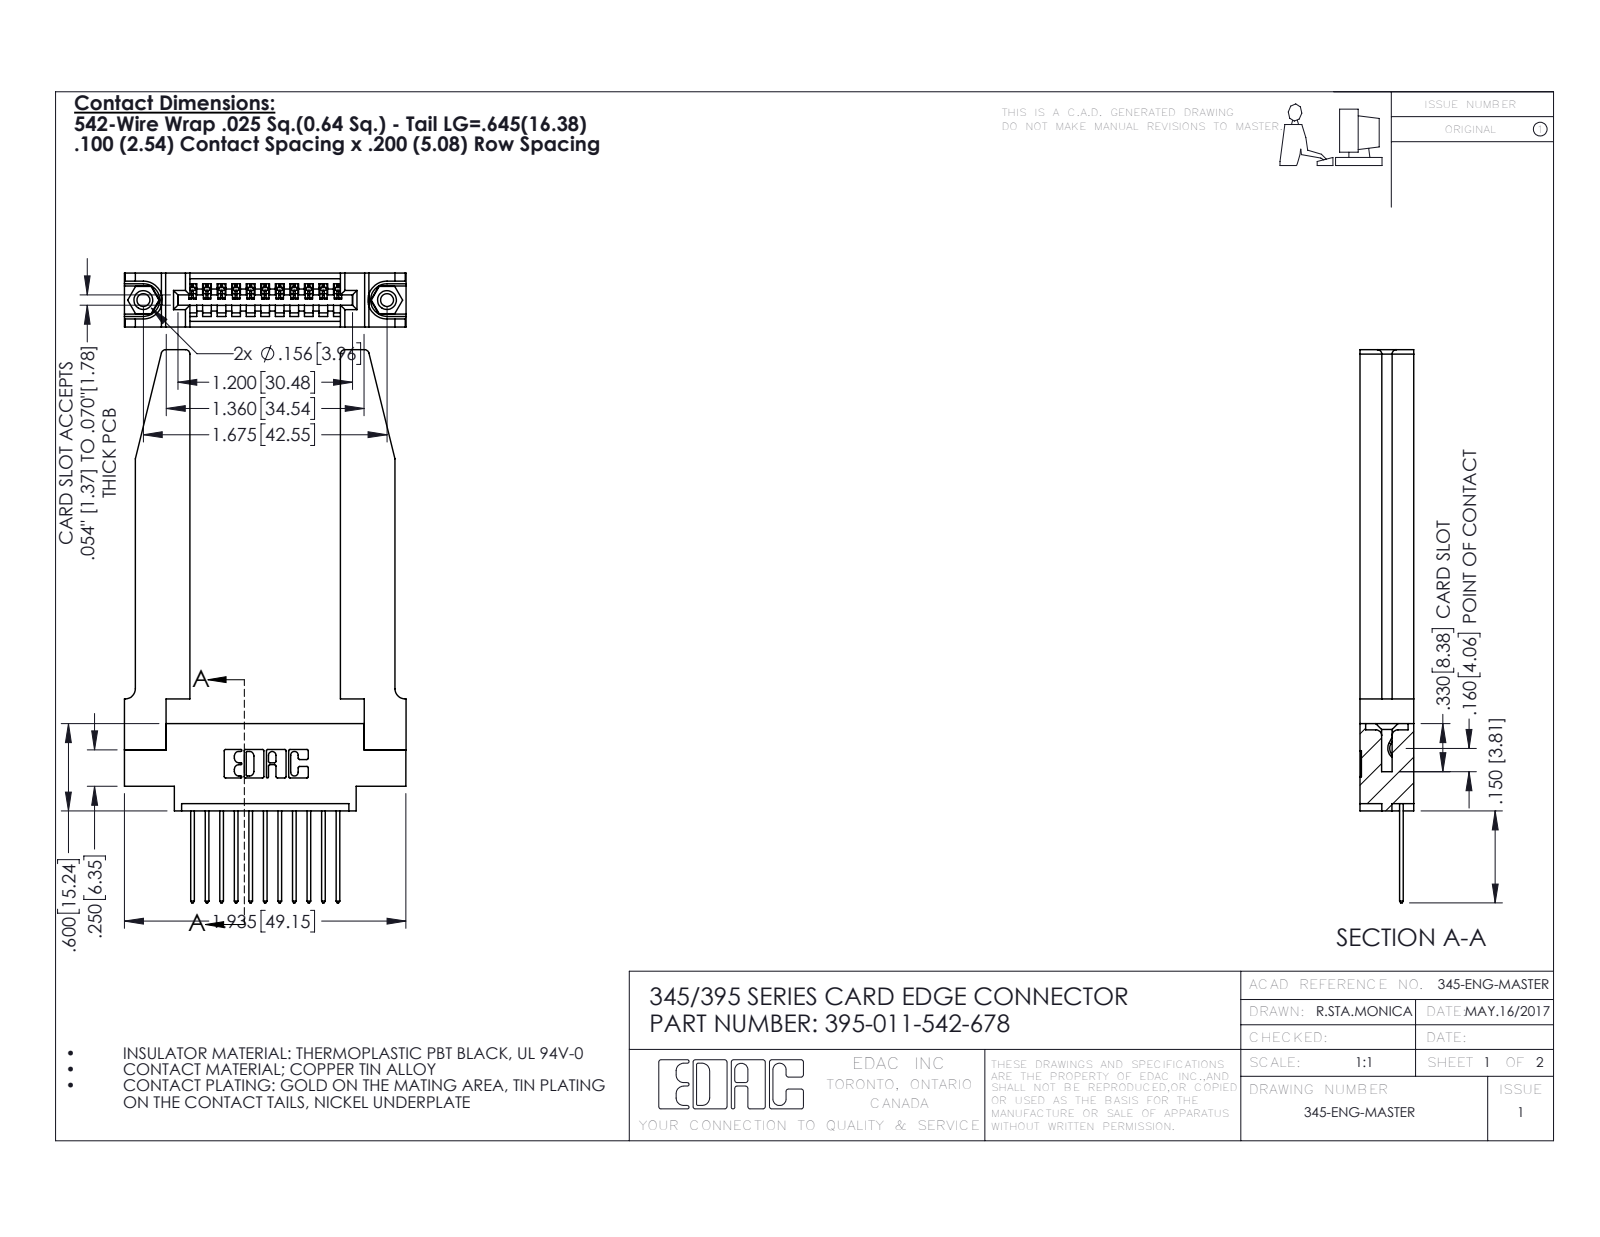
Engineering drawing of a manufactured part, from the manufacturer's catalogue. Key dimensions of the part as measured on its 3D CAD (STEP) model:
Part name (STEP PRODUCT): 345-250-001_345-250-001-102; 345-220-078_345-220-078; 395-011-542-678; 345-292-001_345-293-142 (+1 more)
STEP written by: SolidWorks 2016 (CONFIG_CONTROL_DESIGN)
Units: inches
Bodies: 16 solids, 1002 faces (666 planar, 284 cylindrical, 52 other)
Overall size (bounding box): 3.802 × 1.936 × 0.37
Volume: 0.738 in³ · Surface area: 19.31 in²
Round holes (diameter × count): ⌀0.089 ×2, ⌀0.125 ×2, ⌀0.156 ×2, ⌀0.064 ×1
Round bosses / shafts (diameter × count): ⌀0.155 ×2
Partial cylindrical surfaces — rounded edges, fillets, slot ends (radius × count): R0.006 ×22, R0.01 ×22, R0.01 ×22, R0.03 ×8, R0.007 ×6, R0.031 ×6, R0.026 ×3, R0.031 ×2
Main face-to-face distances: 0.37, 0.072, 0.298, 0.148, 0.15, 0.22, 0.077, 1.035, 0.098, 0.272
Hole centre spacings: 0.27, 1.443, 1.675
